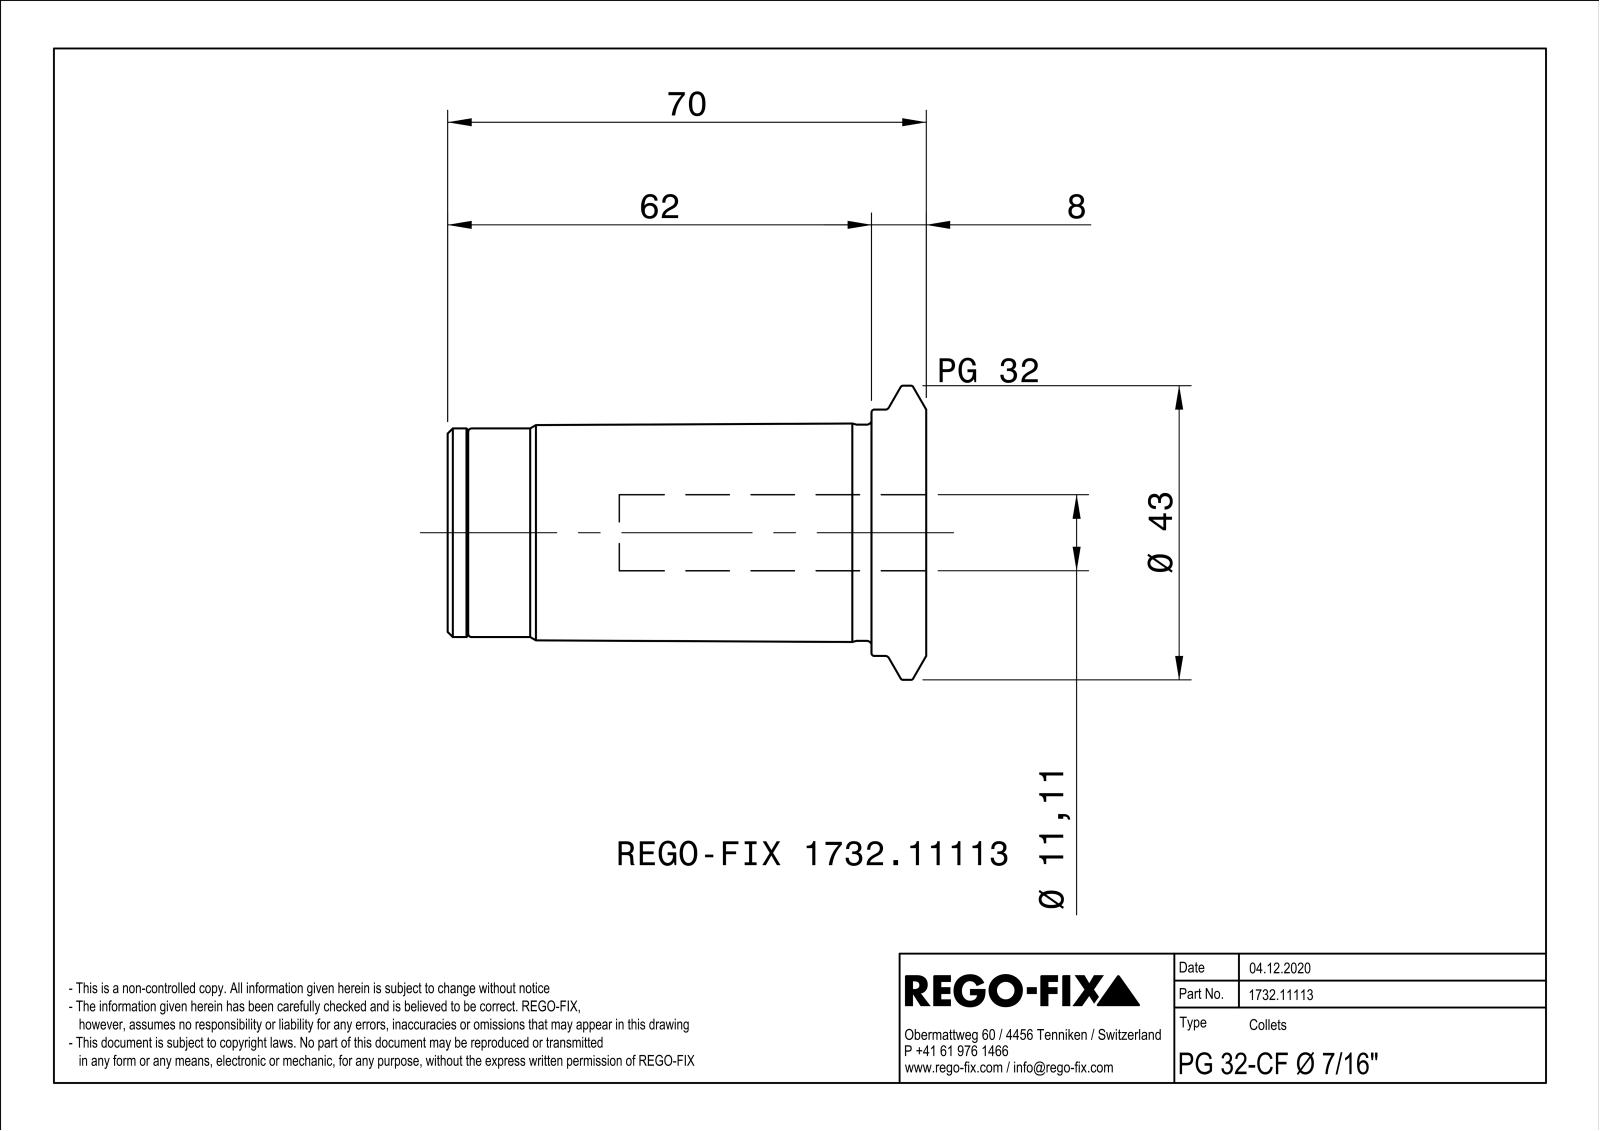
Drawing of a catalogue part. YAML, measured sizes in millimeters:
part_name: "NOCUT"
step_written_by: "SIEMENS PLM Software Solid Edge ST10 (AUTOMOTIVE_DESIGN)"
units: millimeters
bodies: {solids: 1, faces: 132, planar: 31, cylindrical: 46, other: 55}
overall_size: [70, 43, 42.99]
volume: 45877
surface_area: 16809
round_holes:
  - {diameter: 4, count: 3}
  - {diameter: 8.92, count: 1}
  - {diameter: 10.5, count: 1}
  - {diameter: 11.11, count: 1}
  - {diameter: 15.5, count: 1}
  - {diameter: 26.92, count: 1}
  - {diameter: 28.5, count: 1}
round_bosses_or_shafts:
  - {diameter: 43, count: 1}
  - {diameter: 36, count: 1}
  - {diameter: 31.6, count: 1}
  - {diameter: 30.5, count: 1}
  - {diameter: 26.5, count: 1}
  - {diameter: 21, count: 1}
partial_cylinders:
  - {radius: 2, count: 6}
  - {radius: 1, count: 3}
  - {radius: 3.5, count: 3}
  - {radius: 3.98, count: 1}
  - {radius: 4.75, count: 1}
  - {radius: 8.75, count: 1}
face_to_face_distances: [1, 70, 58, 12, 59, 11, 8, 60, 2, 10]
hole_center_spacings: [7.75, 13.42, 13.43]
